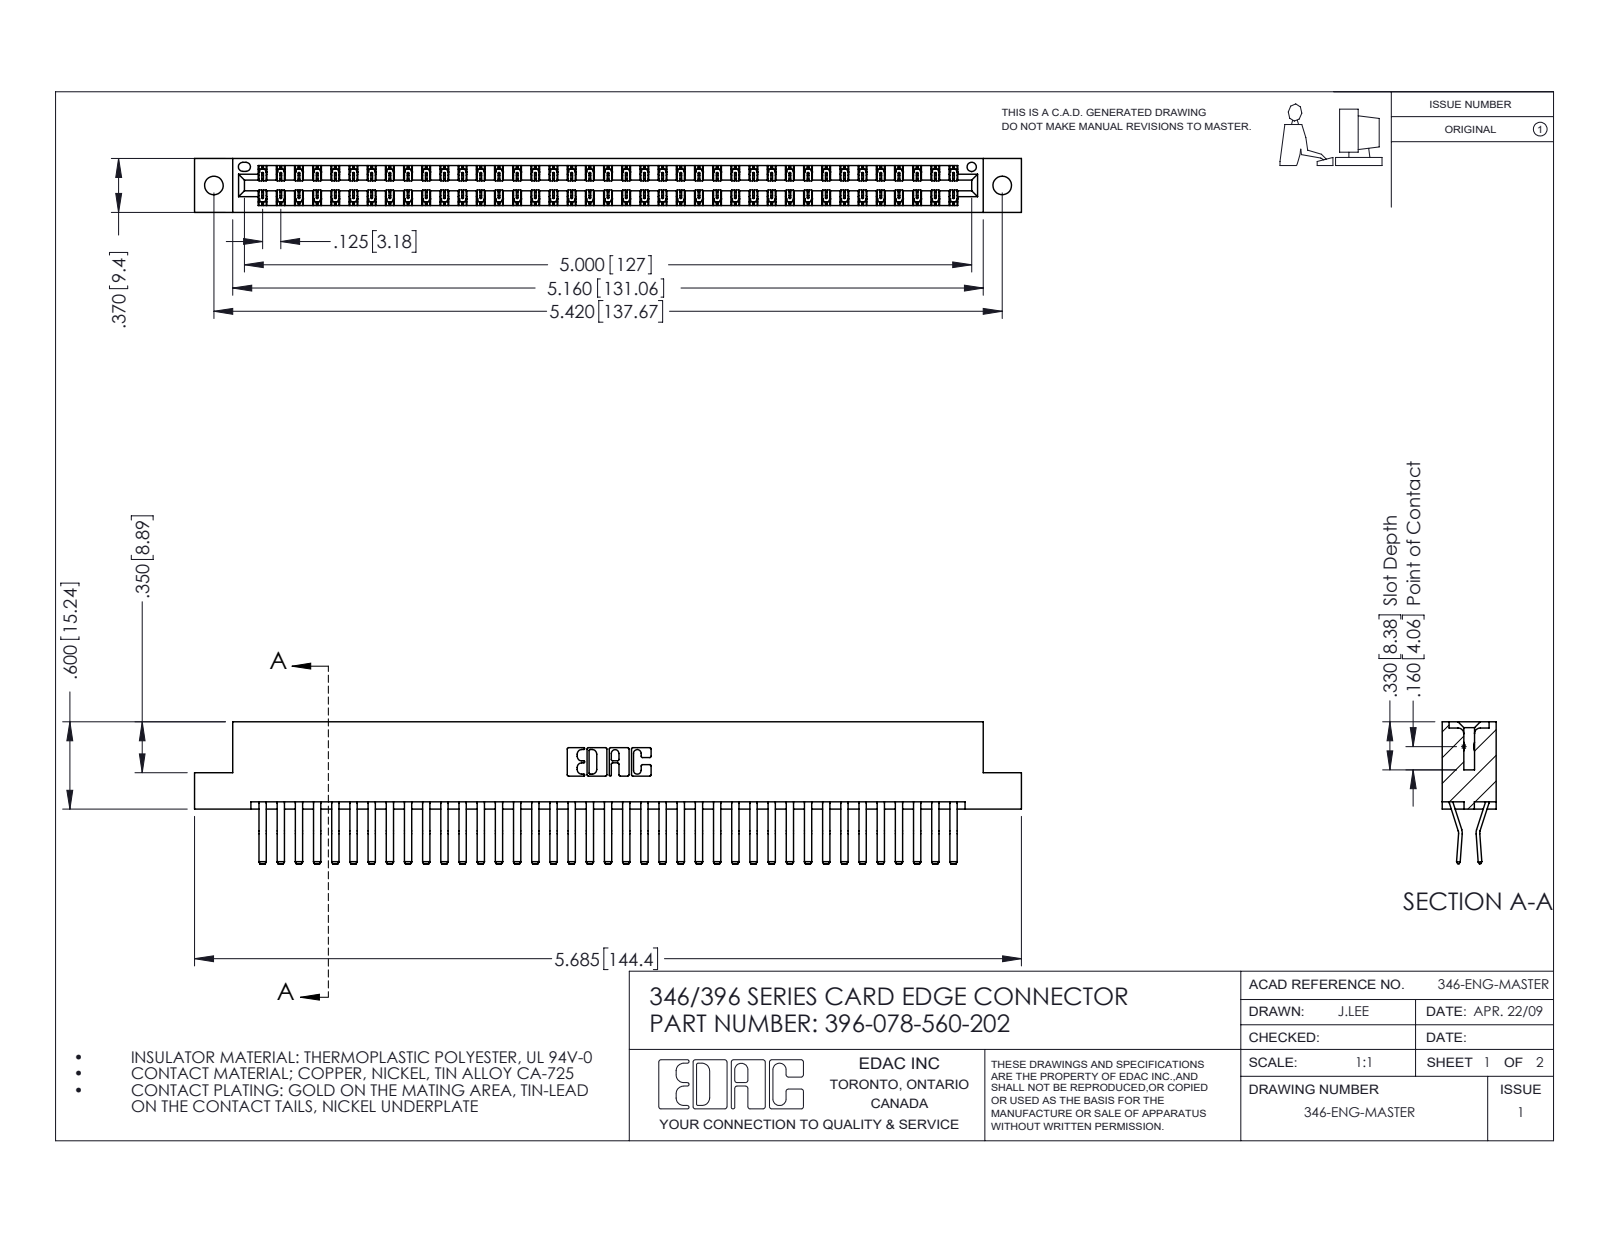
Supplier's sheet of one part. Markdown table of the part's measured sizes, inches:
| quantity | value |
| --- | --- |
| part name | 345-292-001_560 Tail; 346 Part_Flush Mounting Lugs - 0.128 Dia; 396-078-560-202 |
| STEP written by | SolidWorks 2016 (CONFIG_CONTROL_DESIGN) |
| units | inches |
| bodies | 79 solids, 4334 faces (2806 planar, 1528 cylindrical, 0 other) |
| overall size | 5.685 × 0.975 × 0.37 |
| volume | 0.887 in³ |
| surface area | 32.59 in² |
| round holes (diameter × count) | 0.128 × 2, 0.064 × 1 |
| partial cylindrical surfaces (radius × count) | 0.006 × 117, 0.01 × 22, 0.007 × 6, 0.031 × 6, 0.026 × 3, 0.01 × 2, 0.014 × 2, 0.022 × 2 |
| main face-to-face distances | 0.048, 0.322, 0.37, 0.025, 0.25, 0.072, 0.298, 0.275, 0.148, 0.222 |
| hole center spacings | 0.246, 5.211, 5.42 |
